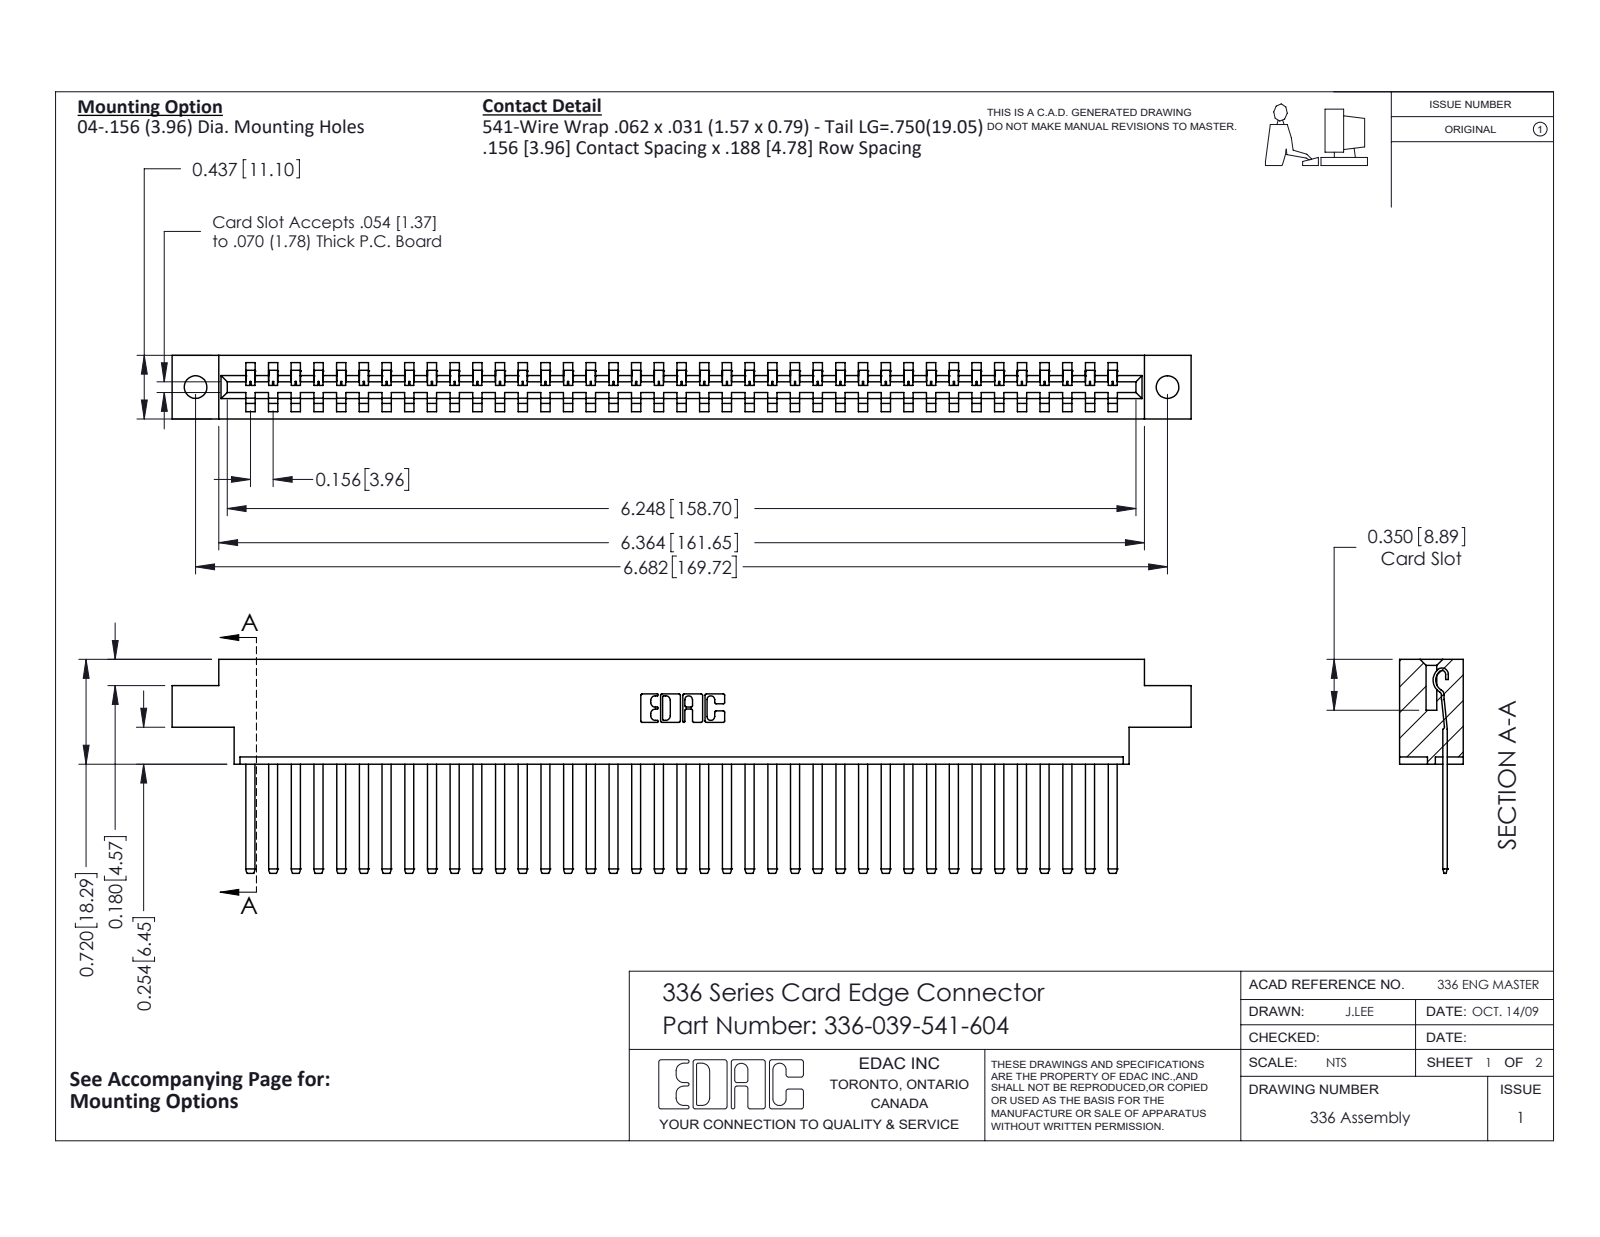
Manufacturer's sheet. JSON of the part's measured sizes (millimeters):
{"part_name": "336-290-001_336-290-541; 336 Part_Offset - .156 Dia - TH; 336-039-541-604", "step_written_by": "SolidWorks 2020 (CONFIG_CONTROL_DESIGN)", "units": "millimeters", "bodies": {"solids": 40, "faces": 2068, "planar": 1400, "cylindrical": 668, "other": 0}, "overall_size": [177.9, 37.3, 11.1], "volume_mm3": 25740, "surface_area_mm2": 27870, "round_holes": [[4, 2]], "partial_cylinders_radius": [[0.1, 78], [1.4, 78], [0.3, 22], [0.2, 6], [0.8, 6], [0.7, 3], [0.6, 2], [1, 2]], "face_to_face_distances": [11.1, 4.6, 8.3, 3.6, 7.5, 2.8, 0.8, 6.5, 1.3, 9.8], "hole_center_spacings": [169.7]}
